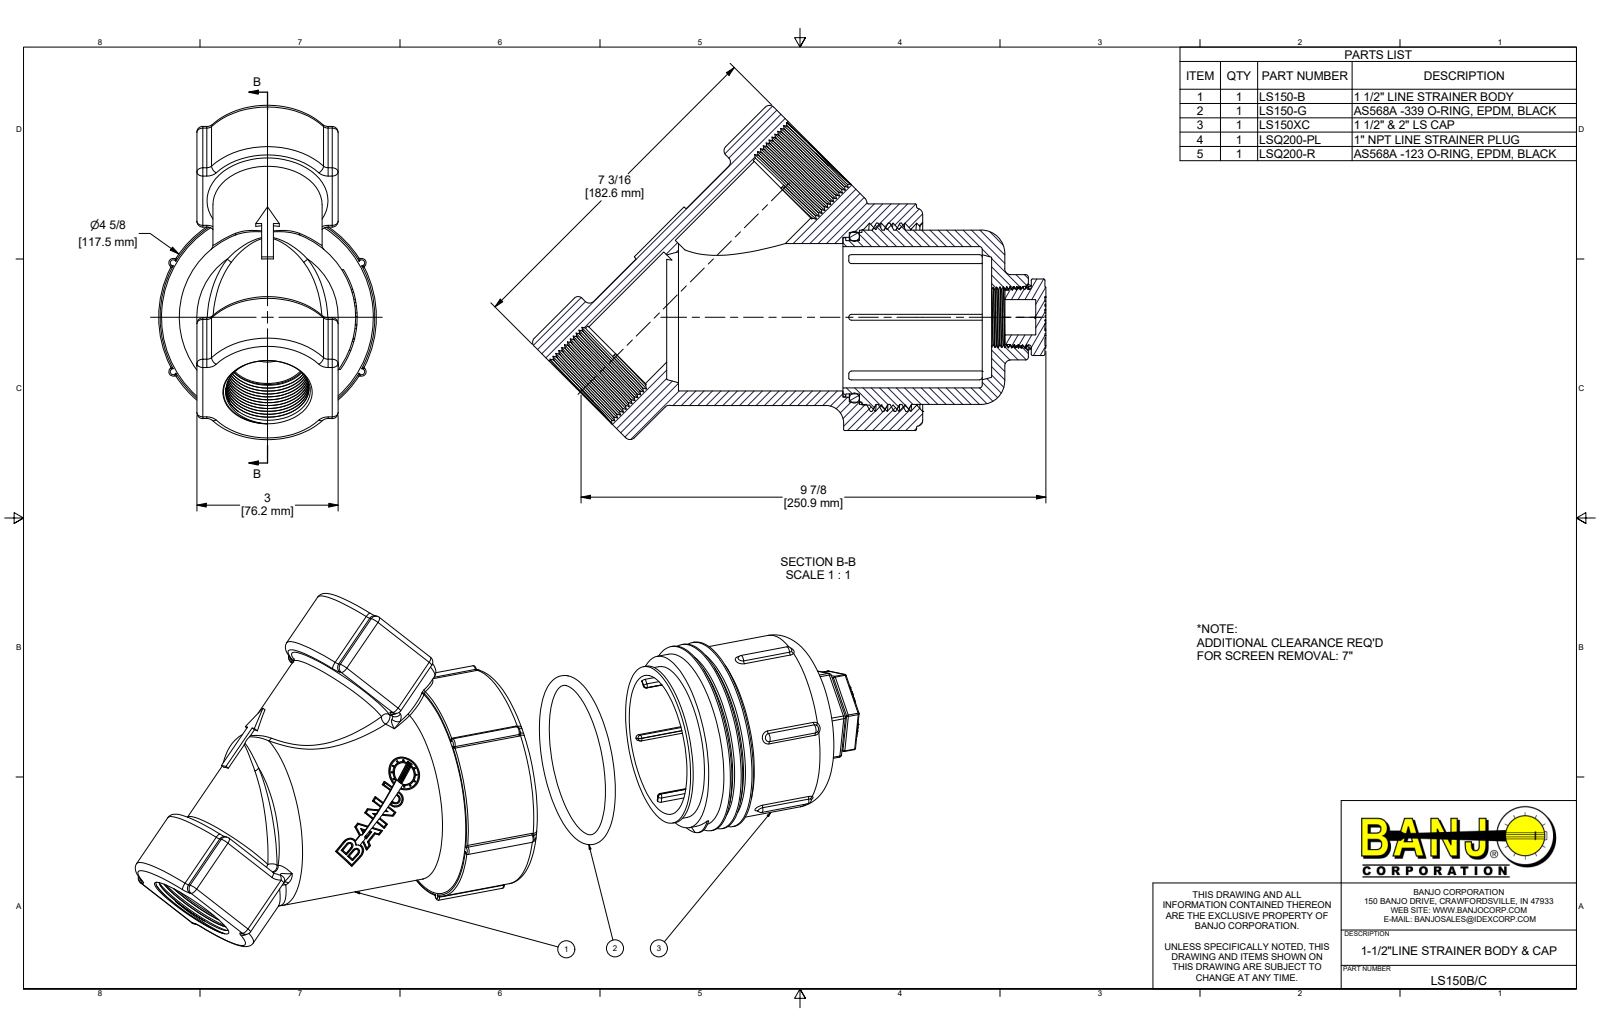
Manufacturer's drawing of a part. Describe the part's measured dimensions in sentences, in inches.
The part is named "LS150-B; LS150XC; LSQ200-PL; LSQ200-R (+3 more)". Its 3-D file was written by "Autodesk Inventor 2016 (AUTOMOTIVE_DESIGN)". It is 4 solids with 1229 faces: 523 planar, 237 cylindrical and 469 other. Overall it measures 10.905 by 7.102 by 4.625 inches. Its volume is 56.16 cubic inches and its surface area 362.2 square inches. Round holes: 2 of diameter 1.7, 2 of diameter 1.761, 1 of diameter 0.454, 1 of diameter 0.641, 1 of diameter 0.75, 1 of diameter 3, 1 of diameter 3.13, 1 of diameter 3.395, 1 of diameter 3.605, 1 of diameter 3.73. Round bosses or shafts: 1 of diameter 4.625, 1 of diameter 4, 1 of diameter 3.75, 1 of diameter 3.702, 1 of diameter 3.38, 1 of diameter 3.257, 1 of diameter 1.315, 1 of diameter 0.675. Partial cylindrical surfaces (rounded edges, fillets, slot ends): 46 of radius 0.06, 35 of radius 0.125, 30 of radius 0.03, 12 of radius 0.094, 3 of radius 0.12, 2 of radius 0.065, 2 of radius 0.082, 2 of radius 0.158. The main face-to-face distances are 3, 7.189, 3.16, 1.465, 1.695, 0.35, 2.81, 1.345, 3.943, 6.903.
